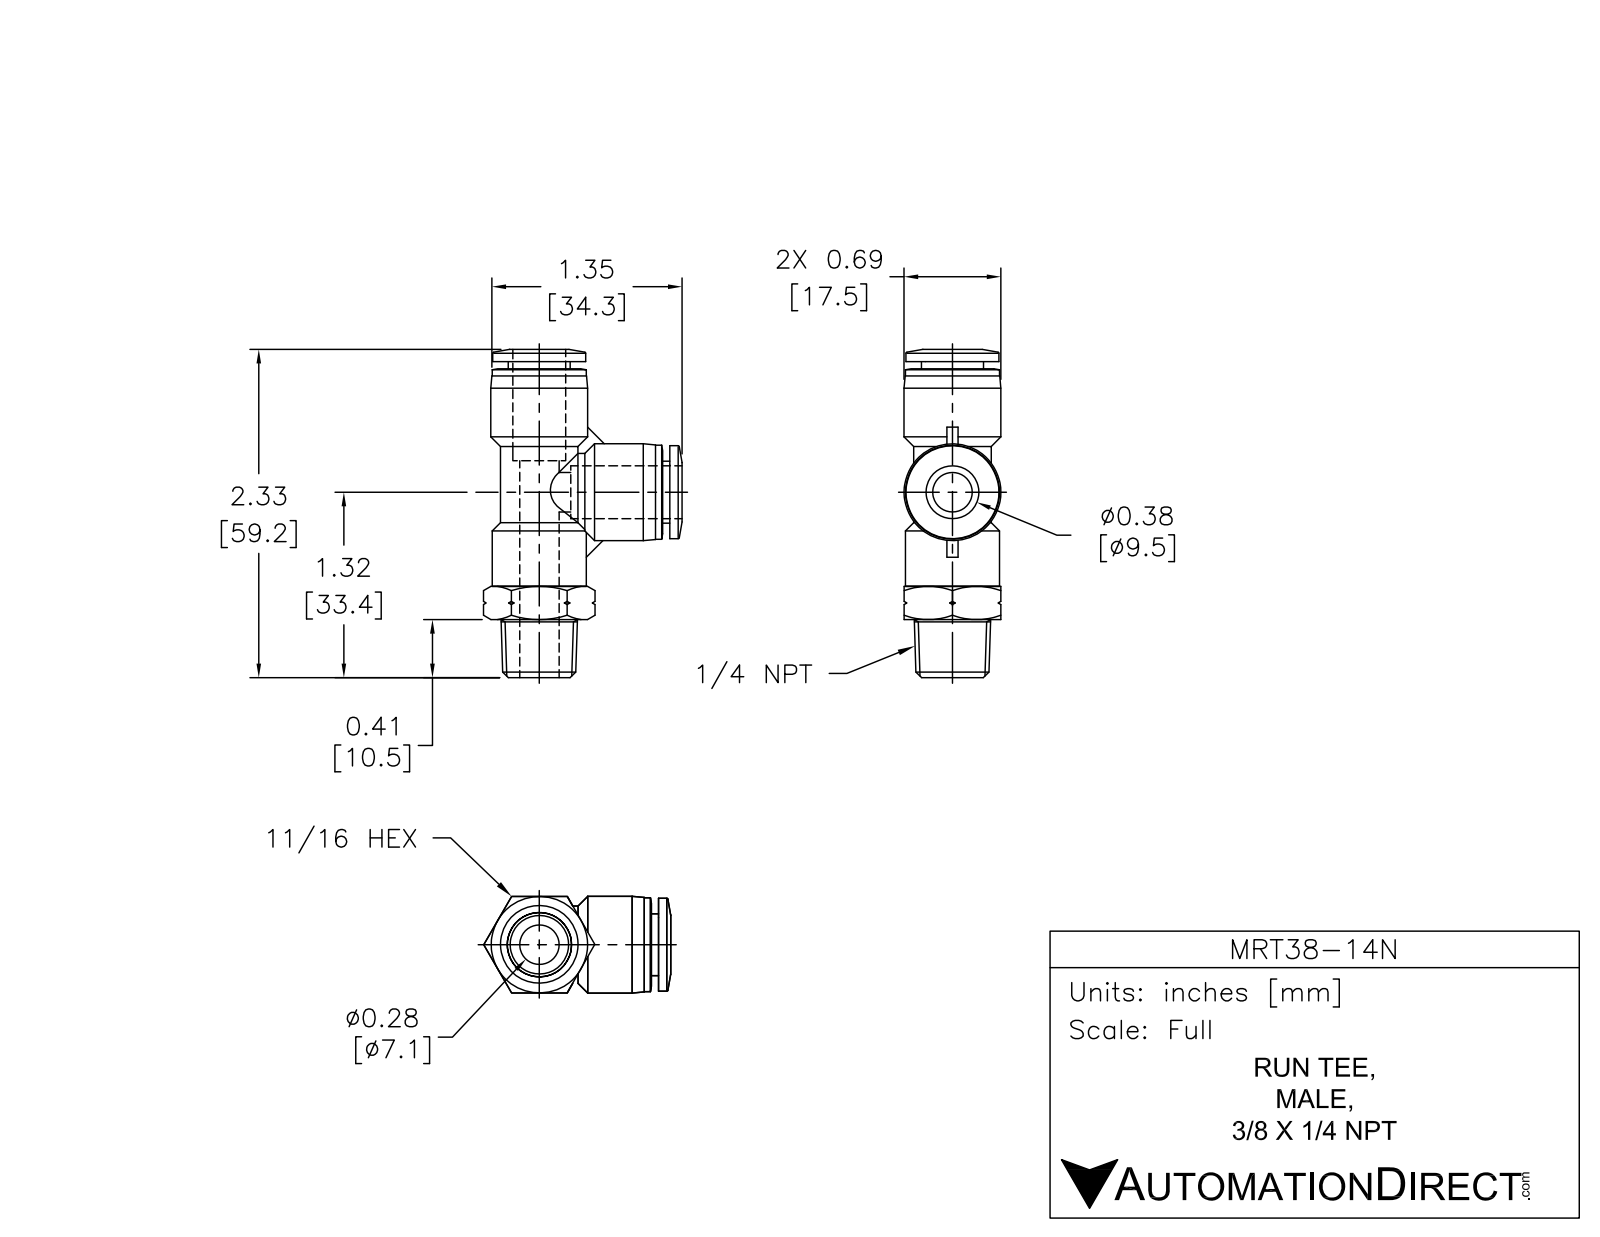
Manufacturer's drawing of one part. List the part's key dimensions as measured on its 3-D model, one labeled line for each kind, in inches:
Part name (STEP PRODUCT): MRT38-14N
STEP written by: SolidWorks 2015 (AUTOMOTIVE_DESIGN)
Units: inches
Bodies: 1 solid, 117 faces (24 planar, 31 cylindrical, 62 other)
Overall size (bounding box): 2.335 × 1.413 × 0.689
Volume: 0.654 in³ · Surface area: 11.02 in²
Round holes (diameter × count): ⌀0.315 ×2, ⌀0.378 ×1, ⌀0.386 ×1
Round bosses / shafts (diameter × count): ⌀0.689 ×2, ⌀0.669 ×2, ⌀0.661 ×2, ⌀0.551 ×2, ⌀0.441 ×2
Main face-to-face distances: 0.687, 0.051, 1.835, 1.783, 0.654, 0.705, 0.413, 2.197, 2.248, 0.304
